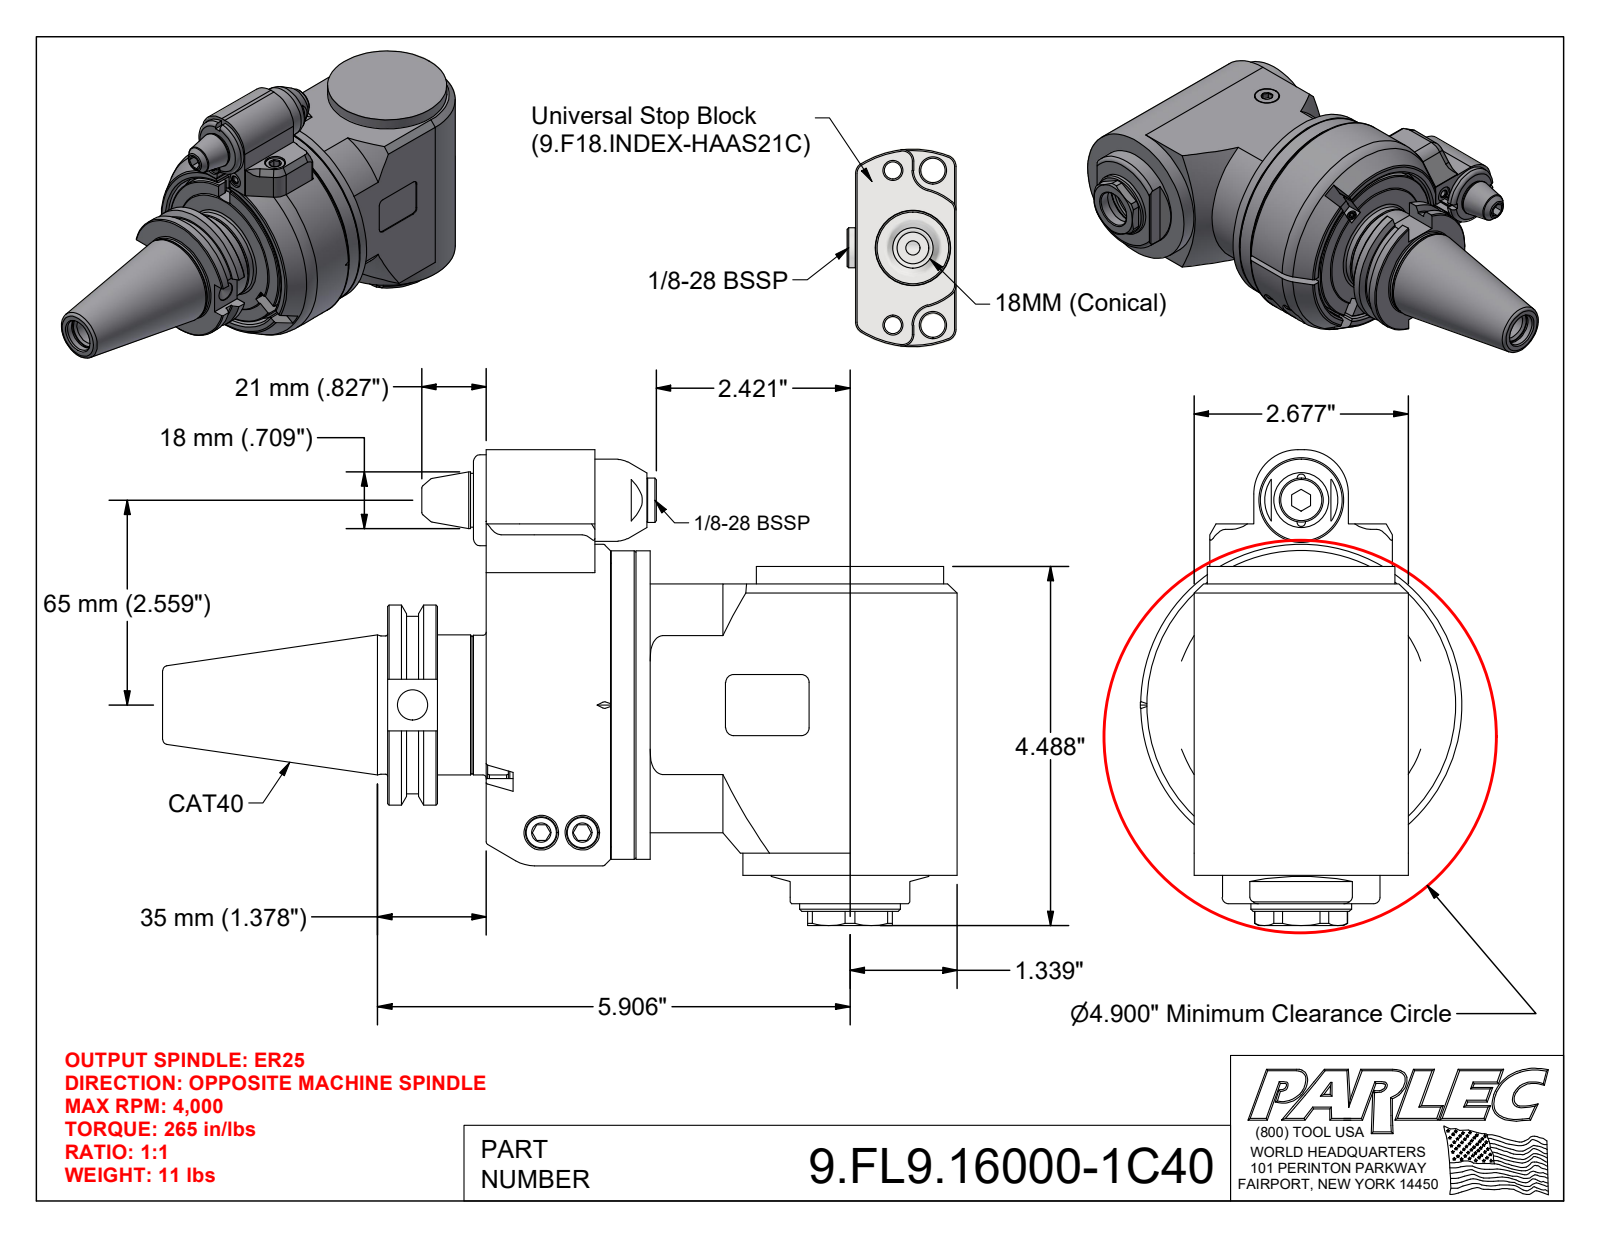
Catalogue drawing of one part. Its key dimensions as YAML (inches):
part_name: "9.FL9.16000-1C40; 9_FL9_16000; 9_GA15C_446 (Type 1, Cat40, 65mm, conical)"
step_written_by: "Autodesk Inventor 2022 (AUTOMOTIVE_DESIGN)"
units: inches
bodies: {solids: 27, faces: 739, planar: 312, cylindrical: 205, other: 222}
overall_size: [9.931, 5.945, 4.016]
volume: 60.13
surface_area: 260.5
round_holes:
  - {diameter: 0.197, count: 7}
  - {diameter: 0.165, count: 6}
  - {diameter: 0.126, count: 4}
  - {diameter: 0.13, count: 4}
  - {diameter: 0.315, count: 4}
  - {diameter: 0.236, count: 3}
  - {diameter: 0.102, count: 2}
  - {diameter: 0.256, count: 2}
  - {diameter: 0.266, count: 2}
  - {diameter: 0.409, count: 2}
  - {diameter: 0.433, count: 2}
  - {diameter: 0.492, count: 2}
round_bosses_or_shafts:
  - {diameter: 0.394, count: 5}
  - {diameter: 0.236, count: 4}
  - {diameter: 0.157, count: 4}
  - {diameter: 0.866, count: 2}
  - {diameter: 0.709, count: 2}
  - {diameter: 0.472, count: 2}
  - {diameter: 0.197, count: 2}
  - {diameter: 4.016, count: 1}
partial_cylinders:
  - {radius: 0.039, count: 14}
  - {radius: 0.118, count: 6}
  - {radius: 0.098, count: 4}
  - {radius: 0.157, count: 4}
  - {radius: 0.02, count: 2}
  - {radius: 0.315, count: 2}
  - {radius: 0.551, count: 2}
  - {radius: 0.581, count: 1}
face_to_face_distances: [0.276, 0.02, 2.677, 0.492, 0.079, 1.555, 1.28, 1.26, 0.197, 2.047]
hole_center_spacings: [0.325, 0.459, 0.276, 0.472, 0.504, 0.65, 0.74, 0.838]
